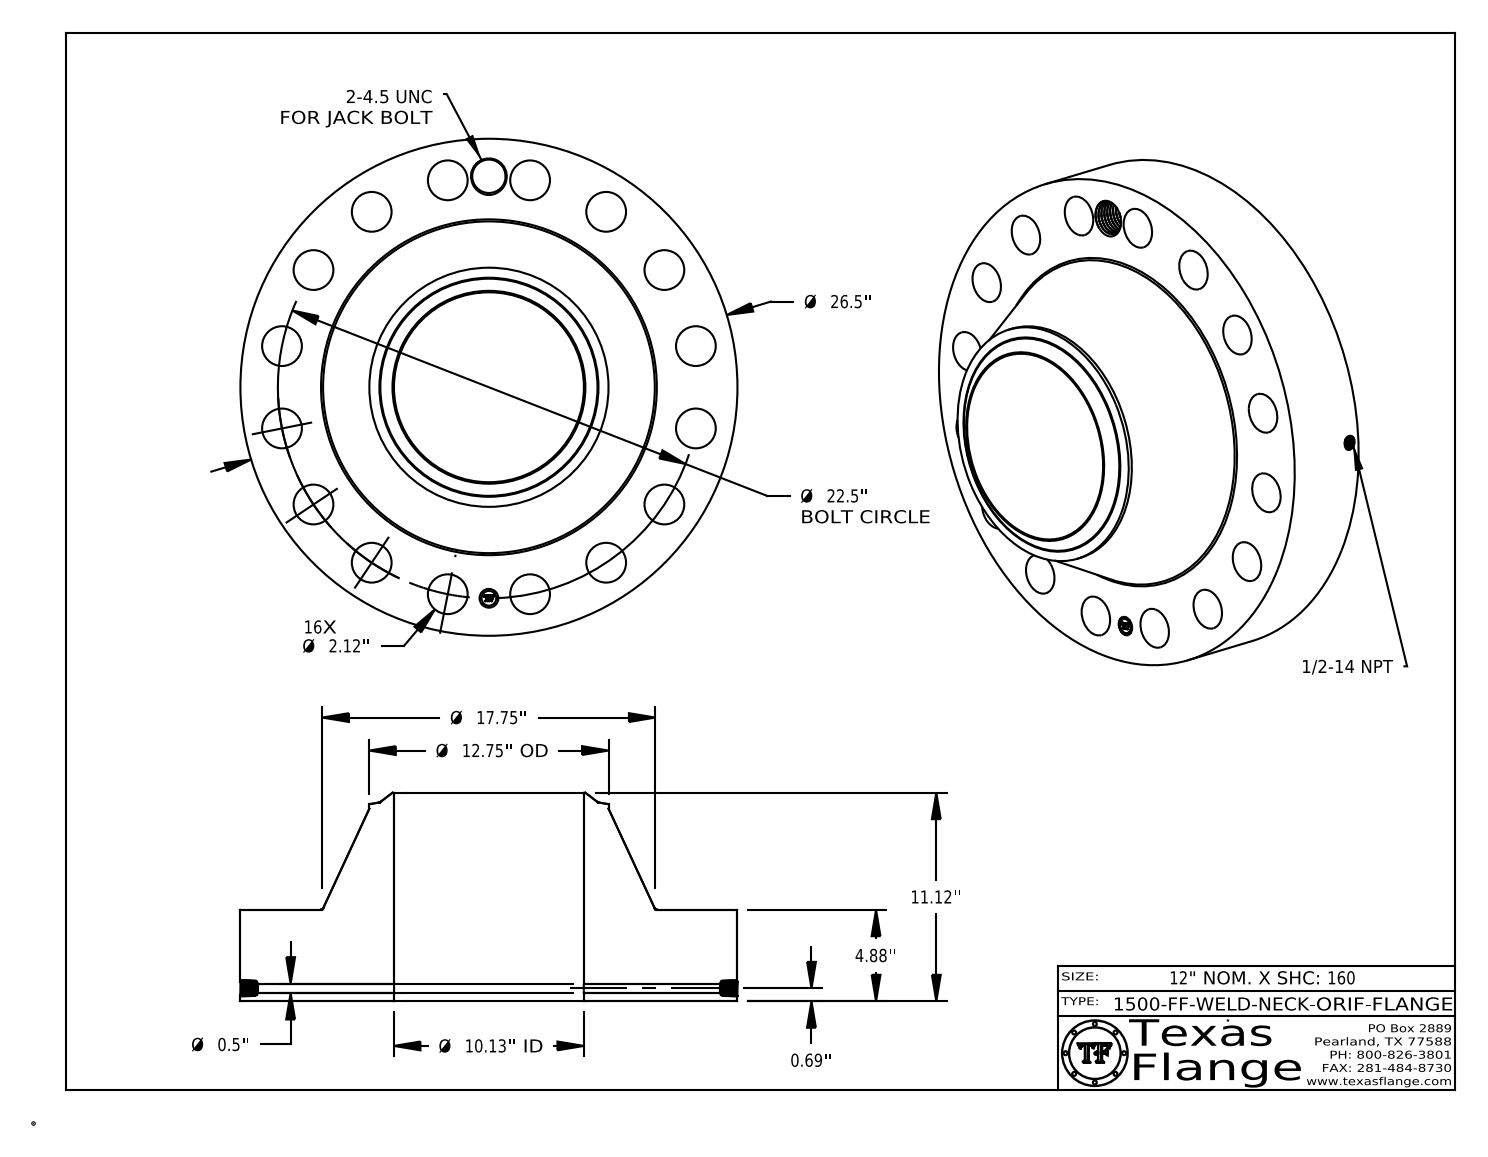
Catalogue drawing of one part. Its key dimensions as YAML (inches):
part_name: "1500-FF-WELD-NECK"
step_written_by: "CATIA V5 STEP AP214 (AUTOMOTIVE_DESIGN)"
units: inches
bodies: {solids: 1, faces: 828, planar: 368, cylindrical: 122, other: 338}
overall_size: [26.5, 26.5, 11.12]
volume: 2587
surface_area: 2353
round_holes:
  - {diameter: 2.12, count: 16}
  - {diameter: 0.5, count: 1}
  - {diameter: 0.672, count: 1}
  - {diameter: 1, count: 1}
  - {diameter: 1.781, count: 1}
  - {diameter: 10.126, count: 1}
round_bosses_or_shafts:
  - {diameter: 0.061, count: 8}
  - {diameter: 26.5, count: 1}
  - {diameter: 12.75, count: 1}
  - {diameter: 0.788, count: 1}
face_to_face_distances: [4.88, 11.12, 6.24, 4.865, 0.015, 6.255, 0.298, 0.293, 0.054, 0.248]
hole_center_spacings: [11.25, 8.61, 15.91, 20.787, 12.5, 18.708, 22.068, 4.389]
